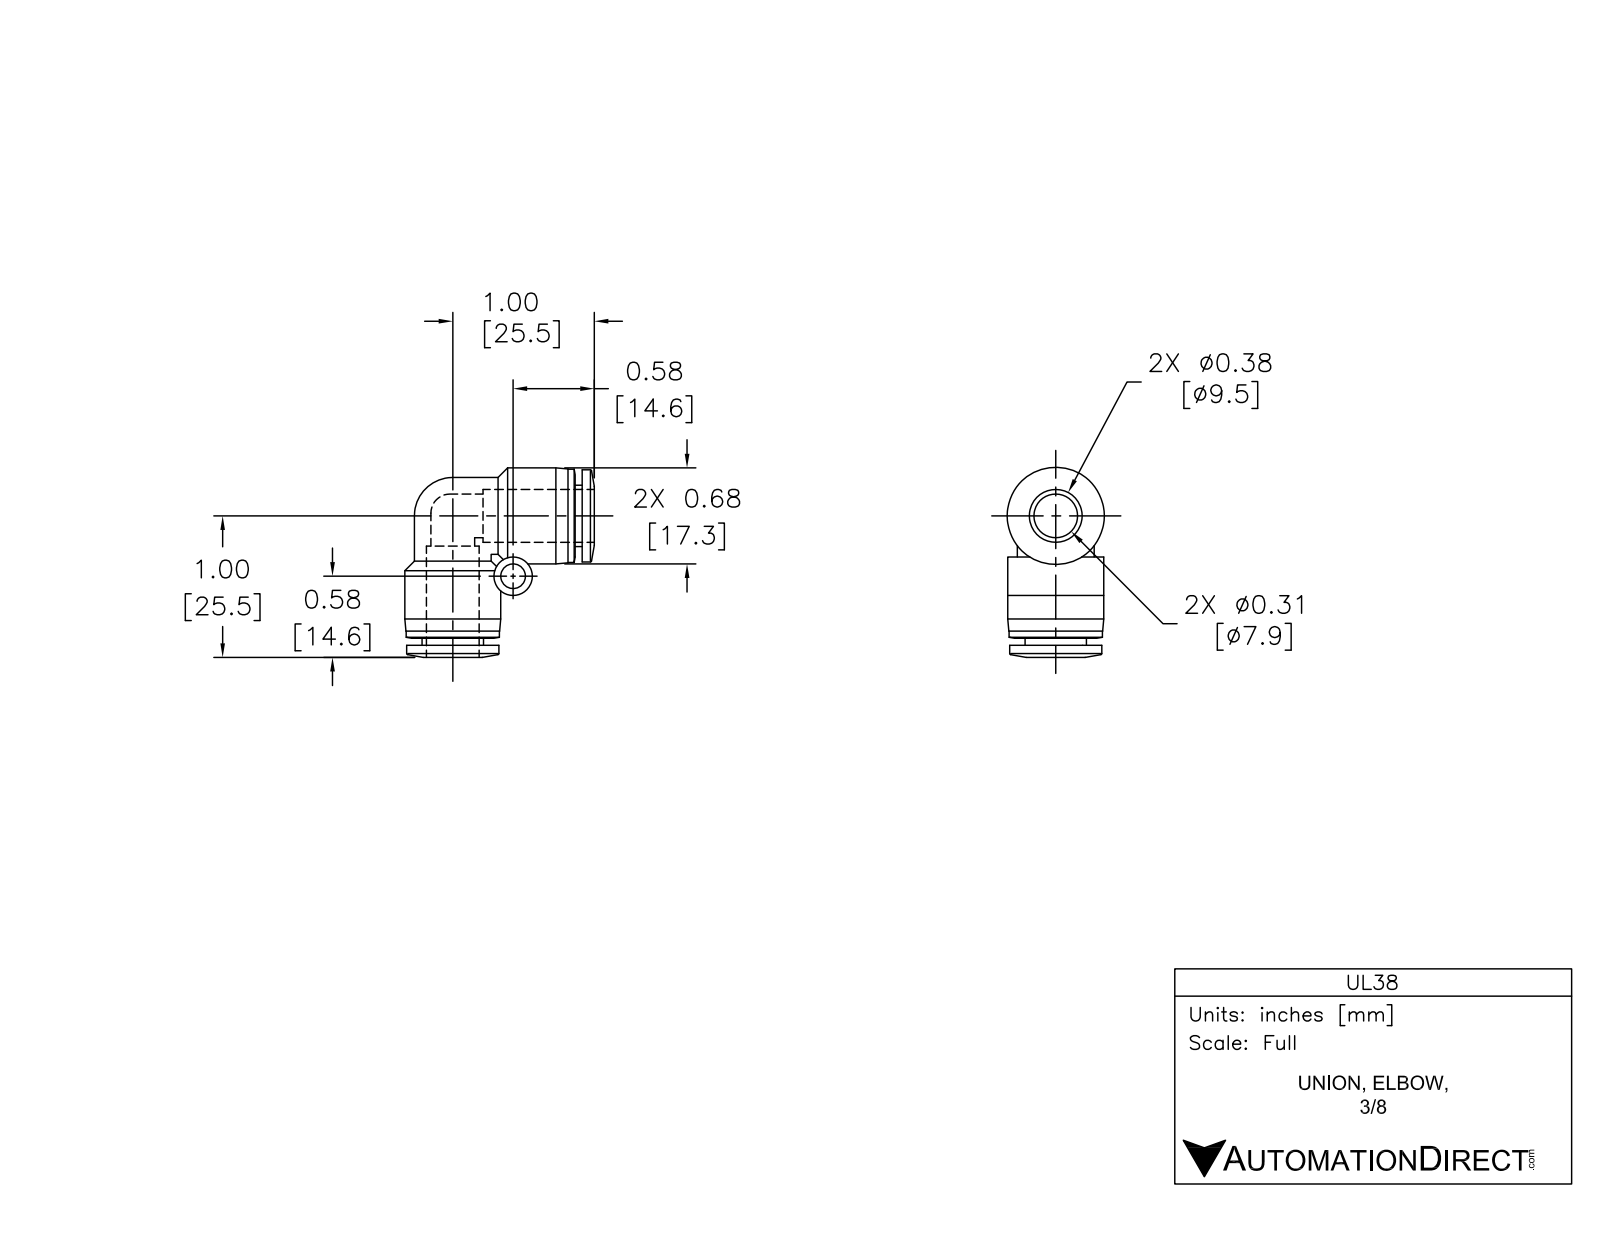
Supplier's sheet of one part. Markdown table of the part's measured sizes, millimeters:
| quantity | value |
| --- | --- |
| part name | UL38 |
| STEP written by | SolidWorks 2015 (AUTOMOTIVE_DESIGN) |
| units | millimeters |
| bodies | 1 solid, 74 faces (10 planar, 32 cylindrical, 32 other) |
| overall size | 34.5 × 34.5 × 17.5 |
| volume | 6 880 mm³ |
| surface area | 5 406 mm² |
| round holes (diameter × count) | 8 × 2, 9.8 × 2, 4.5 × 1 |
| round bosses / shafts (diameter × count) | 17.5 × 2, 17 × 2, 16.8 × 2, 14 × 2, 11.2 × 2, 7 × 1 |
| main face-to-face distances | 1.3, 17.9, 16.6, 16.7, 18, 17.5, 2.6, 15.4, 15.3 |
